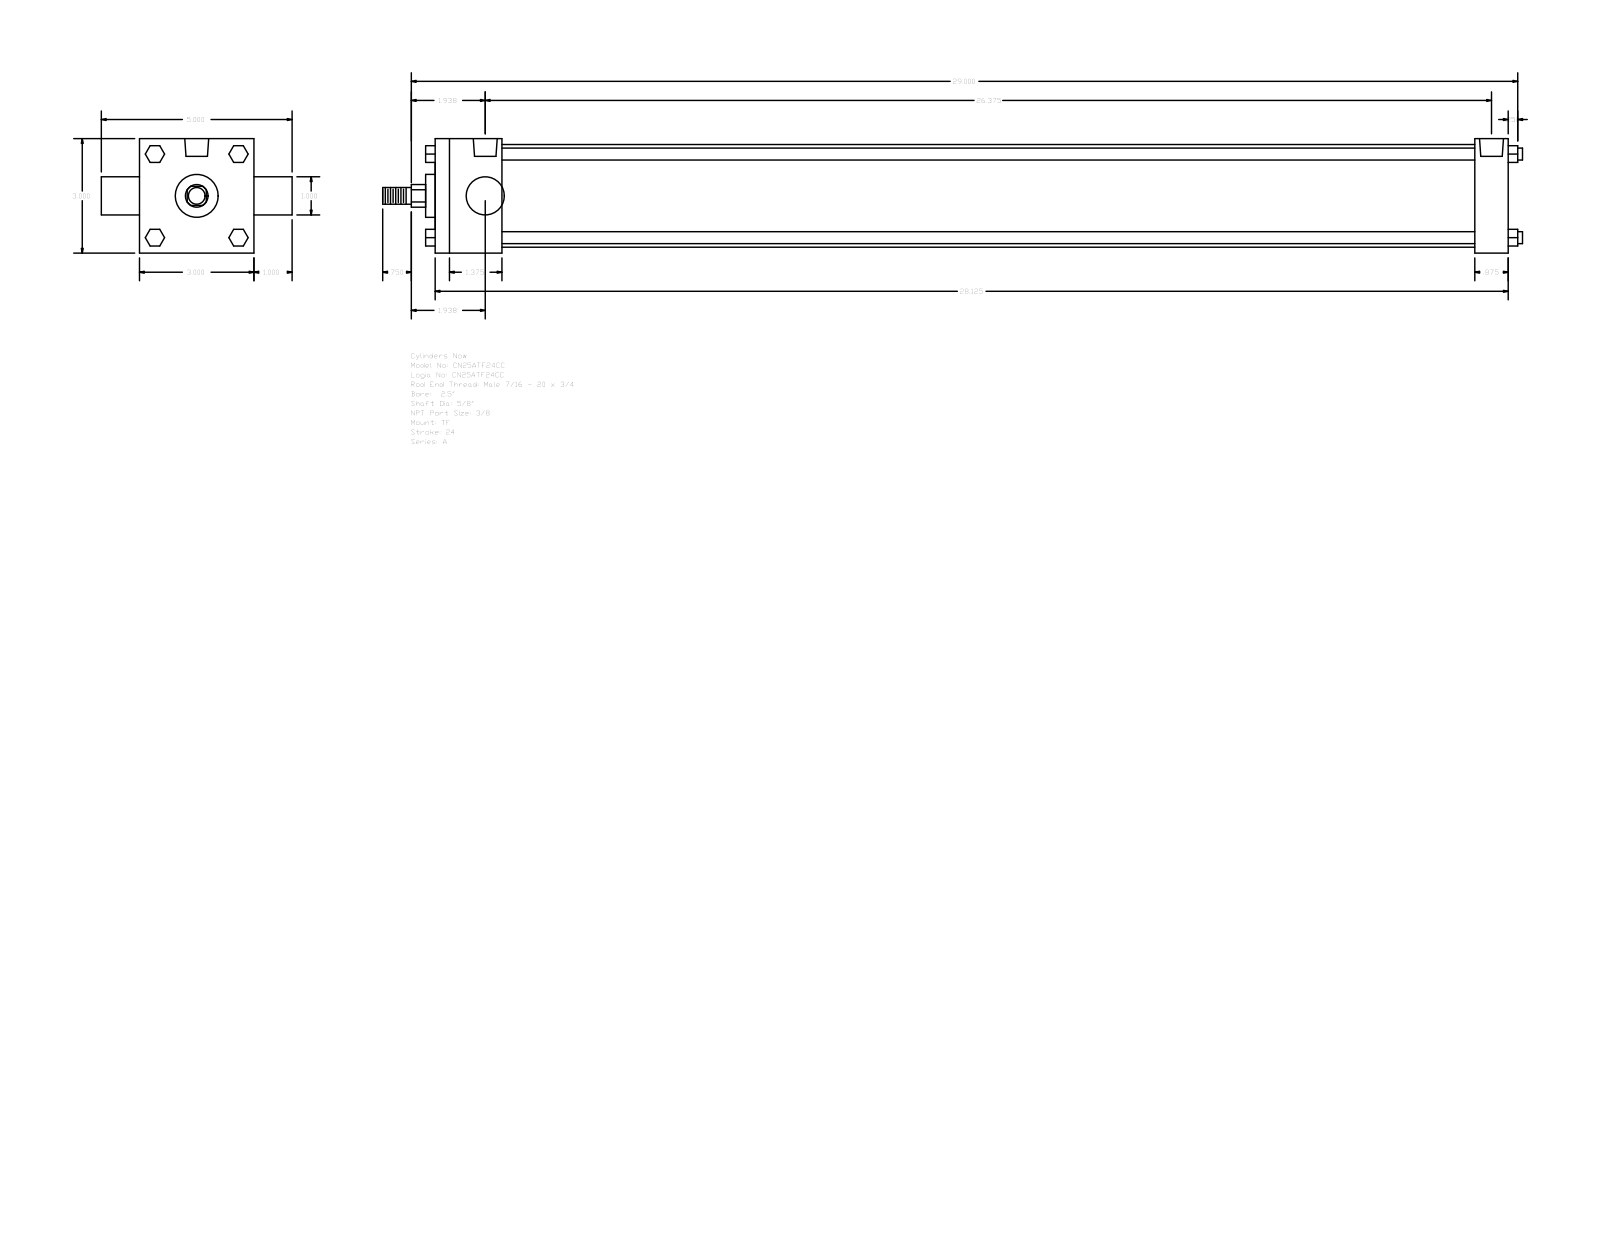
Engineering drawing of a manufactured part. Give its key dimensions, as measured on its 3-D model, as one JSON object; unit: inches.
{"part_name": "A_TF__0250_0.625", "step_written_by": "GSSL Pune (CONFIG_CONTROL_DESIGN)", "units": "inches", "bodies": {"solids": 0, "faces": 120, "planar": 92, "cylindrical": 28, "other": 0}, "overall_size": [29.875, 5, 3], "round_holes": [[0.219, 3], [0.627, 2]], "round_bosses_or_shafts": [[0.313, 4], [2.69, 1], [1.125, 1], [1, 1], [0.625, 1], [0.437, 1]], "partial_cylinders_radius": [[0.297, 1]], "face_to_face_distances": [3, 28.125, 1.75, 27.25, 25.5, 26.375, 0.875, 1, 4, 0.25], "hole_center_spacings": [0.094, 26.469, 26.375, 26.563]}
